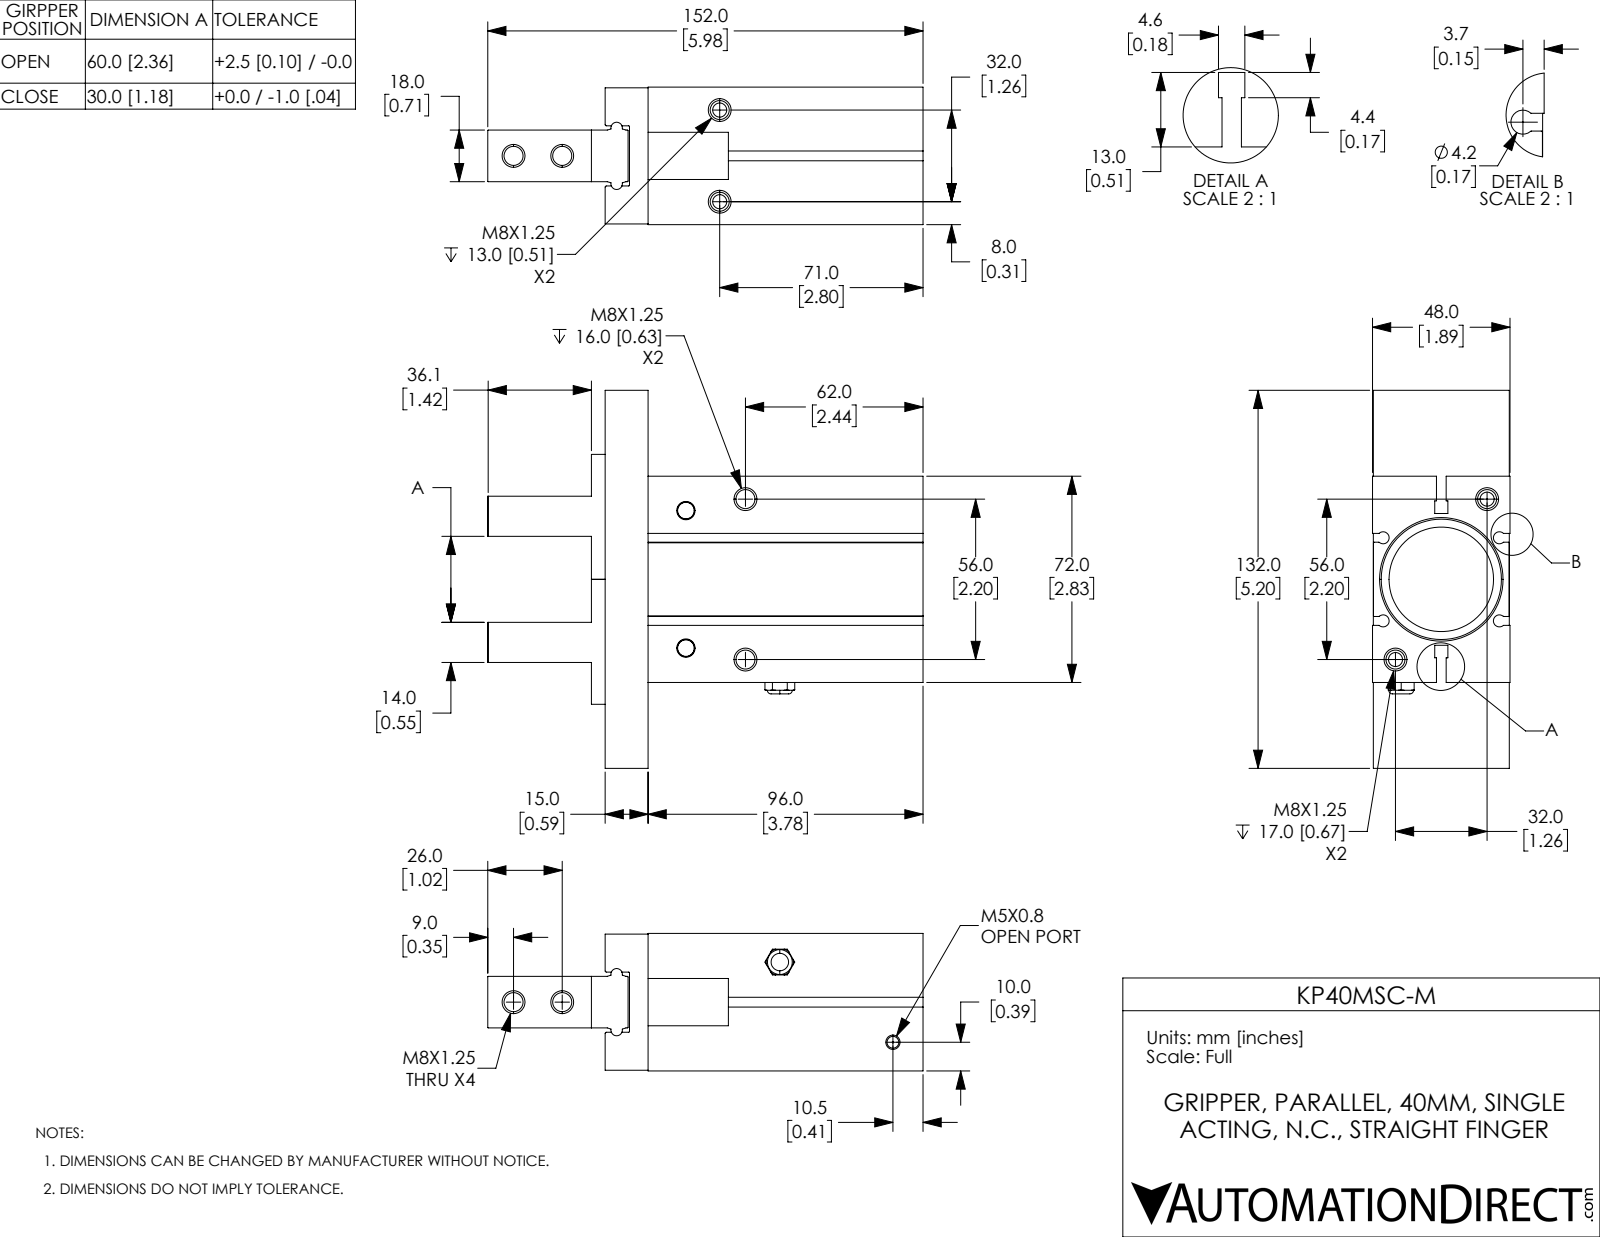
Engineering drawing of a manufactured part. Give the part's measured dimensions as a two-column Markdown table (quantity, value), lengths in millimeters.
| quantity | value |
| --- | --- |
| part name | KP40MSC-M; KP40MSC-M-1; KP40MSC-M-2; KP40MSC-M-3 |
| STEP written by | SolidWorks 2017 (CONFIG_CONTROL_DESIGN) |
| units | millimeters |
| bodies | 3 solids, 262 faces (127 planar, 65 cylindrical, 70 other) |
| overall size | 152 × 132 × 48 |
| volume | 379 092 mm³ |
| surface area | 72 412 mm² |
| round holes (diameter × count) | 6.65 × 5, 6.65 × 3, 0.5 × 2, 4.13 × 2, 8.02 × 2, 6.1 × 1, 36.5 × 1, 42 × 1 |
| partial cylindrical surfaces (radius × count) | 0.2 × 7, 2.1 × 4, 0.3 × 2, 2 × 2 |
| main face-to-face distances | 15, 47.7, 15.75, 32.25, 15.45, 31.95, 47.75, 15.5, 32, 47.45 |
| hole center spacings | 32.25, 57.28, 73.76, 17, 21.1, 32, 36.62, 48.42 |
